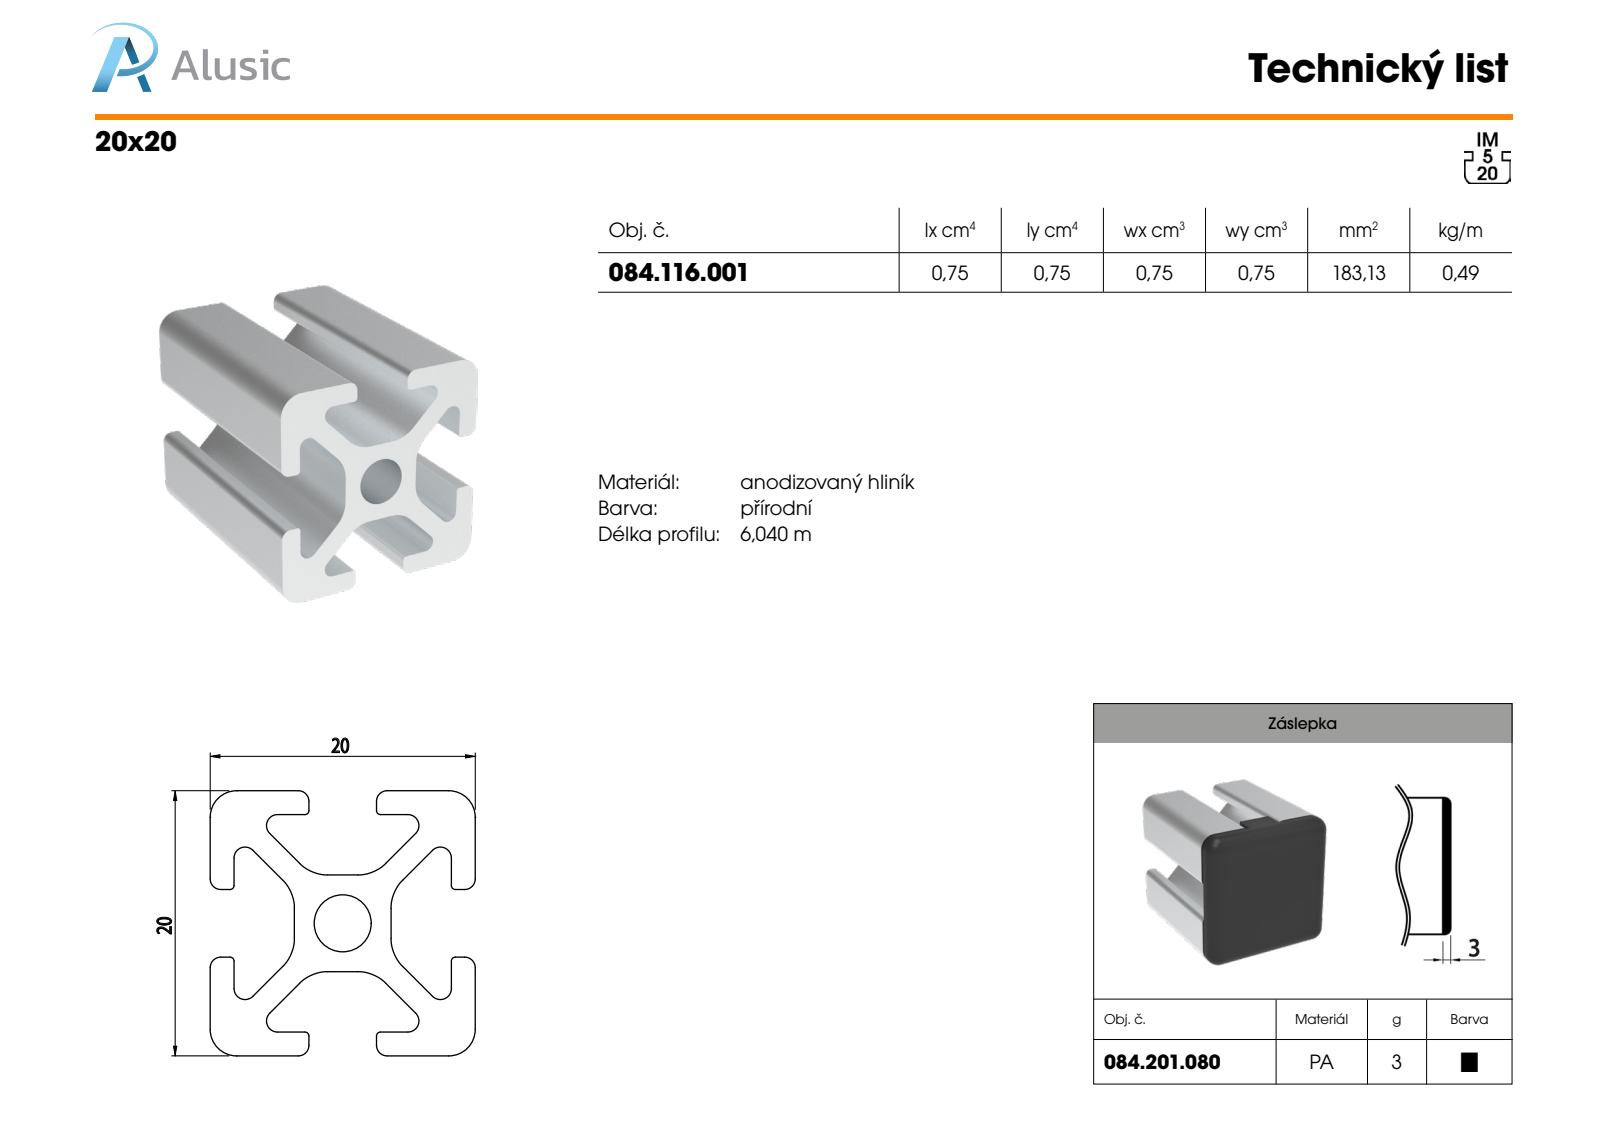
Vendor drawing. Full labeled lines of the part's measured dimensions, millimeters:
Part name (STEP PRODUCT): 084.116.001
STEP written by: SolidWorks 2018 (AUTOMOTIVE_DESIGN)
Units: millimetres
Bodies: 1 solid, 78 faces (38 planar, 40 cylindrical, 0 other)
Overall size (bounding box): 100 × 20 × 20
Volume: 18 313 mm³ · Surface area: 17 198 mm²
Round holes (diameter × count): ⌀4.3 ×1
Partial cylindrical surfaces — rounded edges, fillets, slot ends (radius × count): R0.3 ×8, R0.8 ×8, R0.83 ×8, R3 ×8, R2 ×4
Main face-to-face distances: 1.8, 20, 18.2, 6.35, 13.65, 4.55, 11.85, 16.4, 7.45, 12.55
